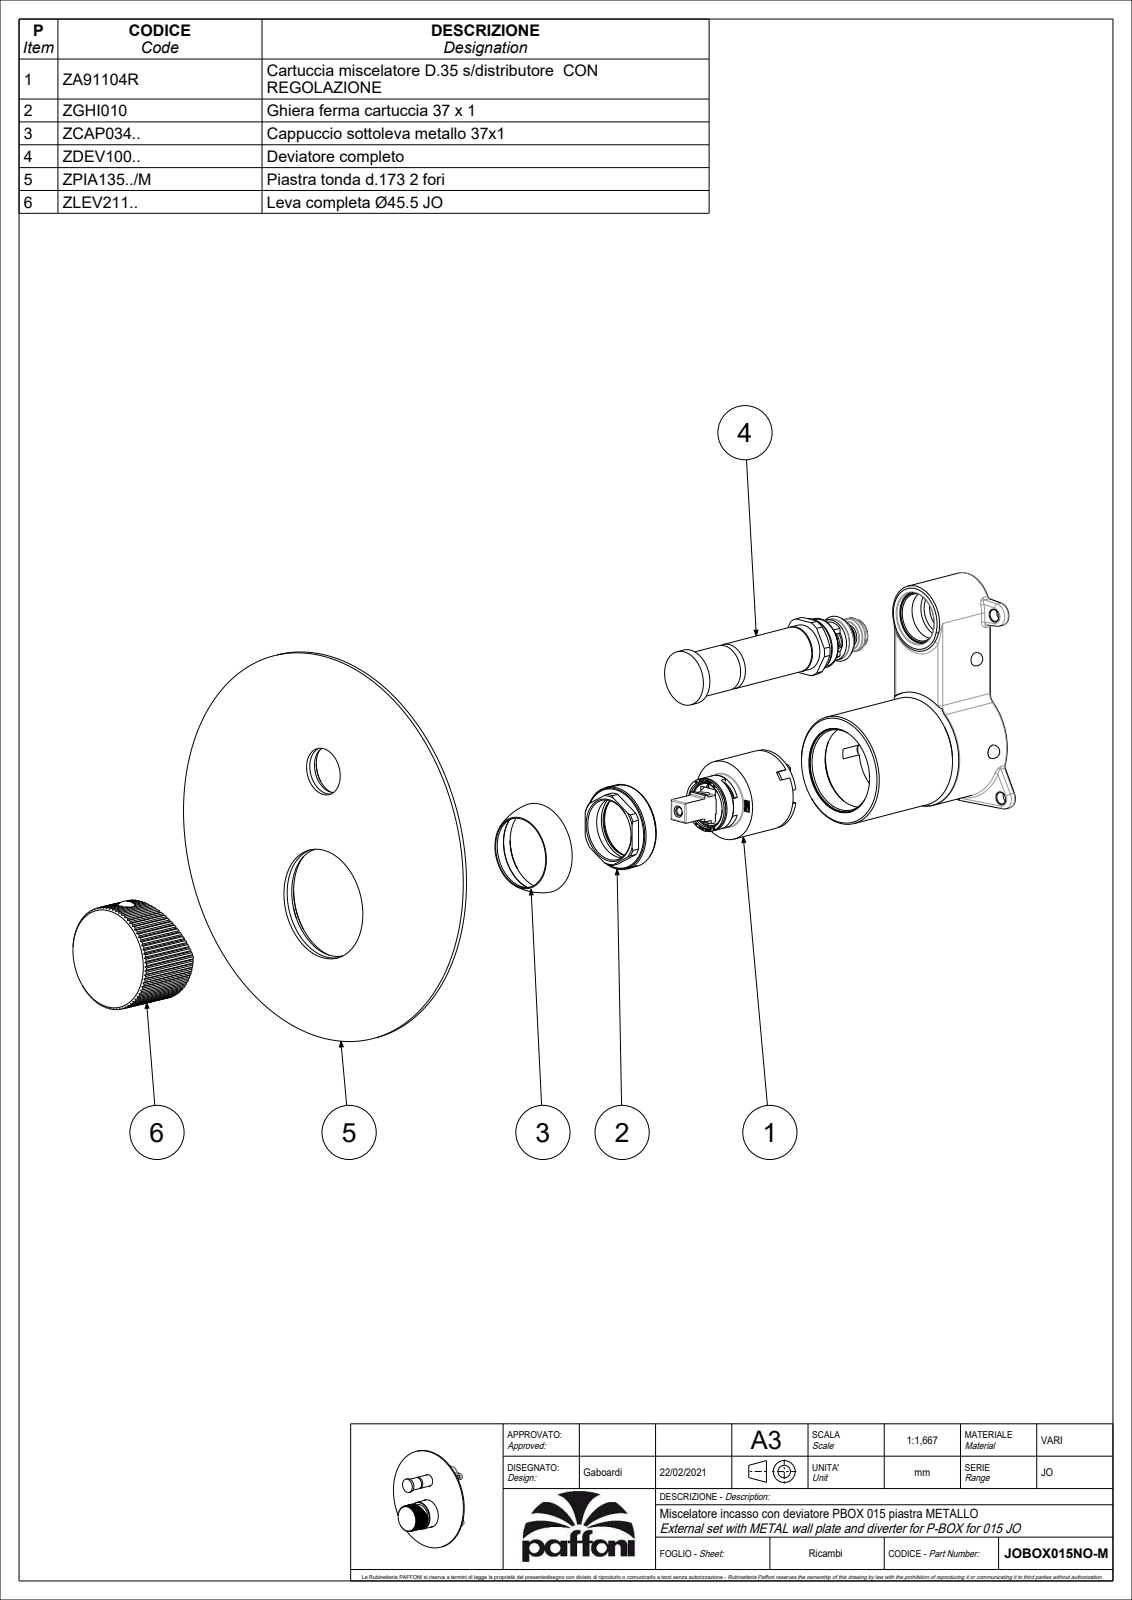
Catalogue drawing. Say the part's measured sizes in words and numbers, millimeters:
The part is named "JOBOX015NO-M". Its 3-D file was written by "CREO PARAMETRIC BY PTC INC, 2020044 (CONFIG_CONTROL_DESIGN)". It is 4 solids with 1128 faces: 718 planar, 277 cylindrical and 133 other. Overall it measures 173 by 173 by 55.5 millimeters. Its volume is 102 172 cubic millimeters and its surface area 86 457 square millimeters. Round holes: 2 of diameter 4, 1 of diameter 3, 1 of diameter 3.3, 1 of diameter 5, 1 of diameter 5.5, 1 of diameter 7.1, 1 of diameter 10.5, 1 of diameter 16, 1 of diameter 18.2, 1 of diameter 19.5, 1 of diameter 19.9, 1 of diameter 20.8. Round bosses or shafts: 1 of diameter 173, 1 of diameter 48.1, 1 of diameter 35, 1 of diameter 24, 1 of diameter 23.5, 1 of diameter 23.4, 1 of diameter 21.8, 1 of diameter 20. Partial cylindrical surfaces (rounded edges, fillets, slot ends): 11 of radius 0.15, 6 of radius 0.5, 4 of radius 0.3, 2 of radius 1, 1 of radius 2.5, 1 of radius 4, 1 of radius 6.5, 1 of radius 7. The main face-to-face distances are 2, 52.1, 50.1, 23, 29.1, 5.5, 9, 6, 21, 17.5. The hole center spacings are 13, 60.
